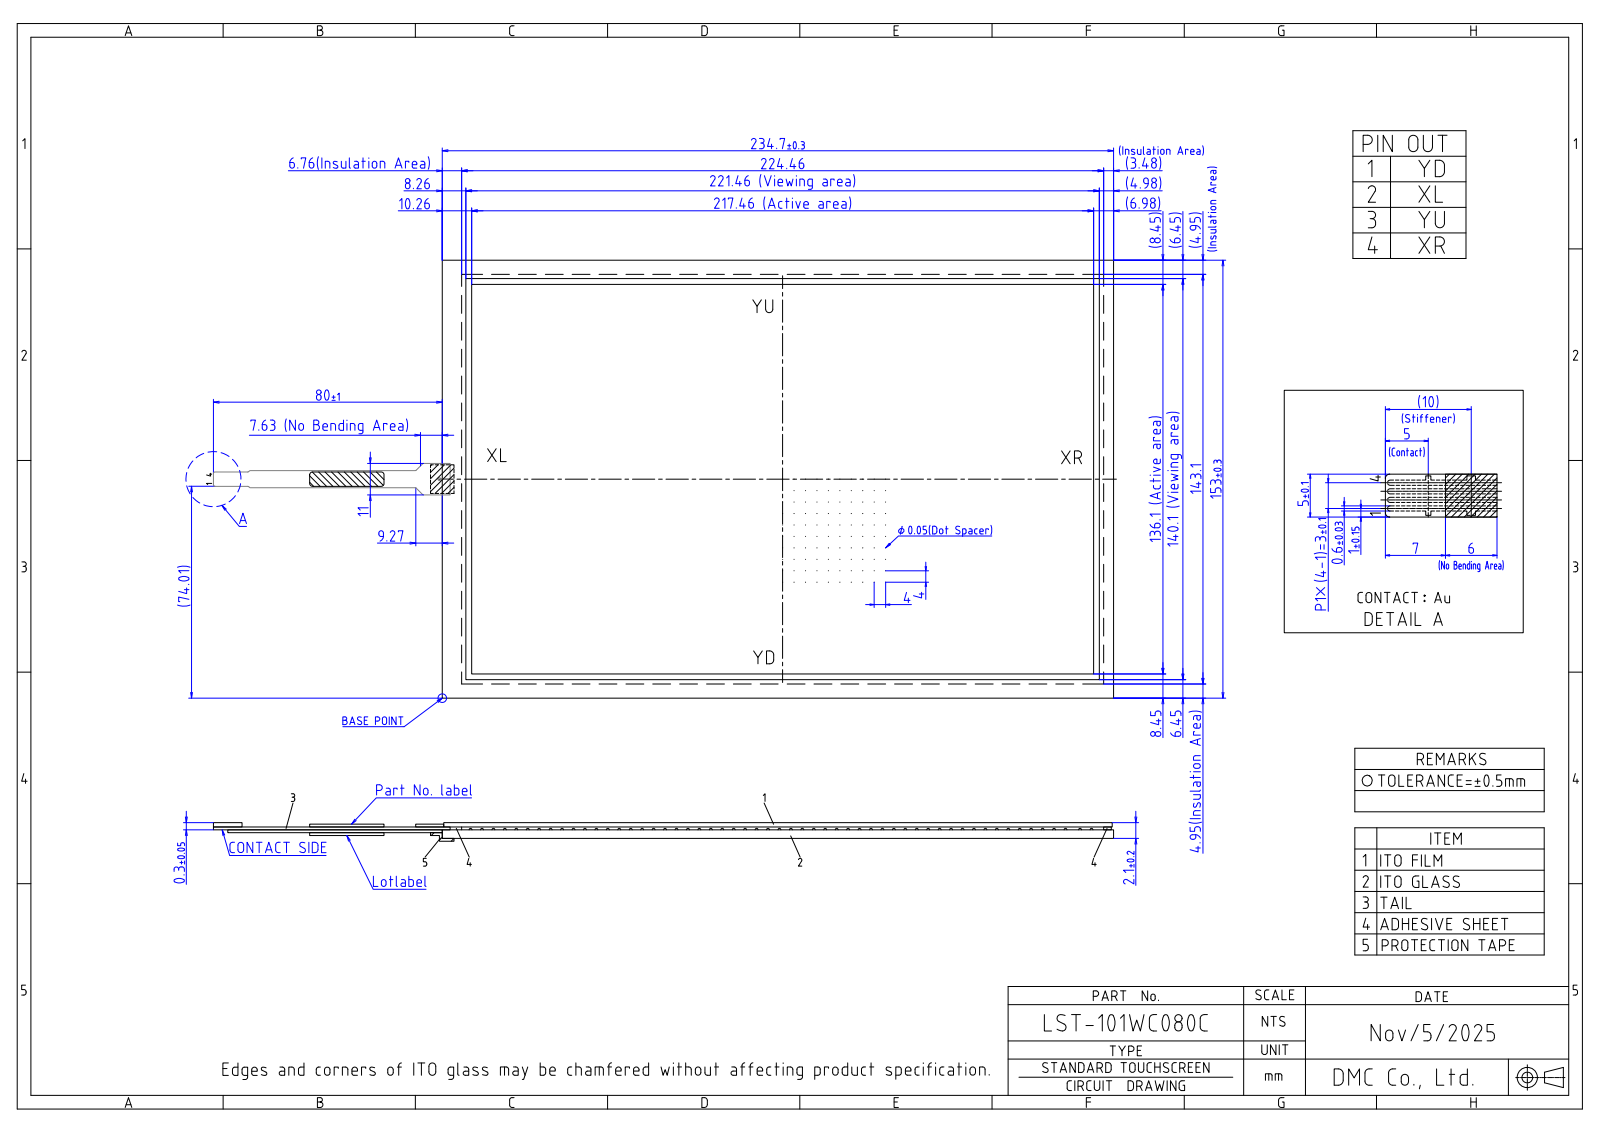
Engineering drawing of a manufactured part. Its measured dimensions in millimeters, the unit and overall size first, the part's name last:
Units: millimetres
Overall size (bounding box): 361.64 × 214.2 × 2.6
Partial cylindrical surfaces — rounded edges, fillets, slot ends (radius × count): R0.3 ×4, R0.5 ×2
Main face-to-face distances: 2.1, 2, 153, 2.2, 2.3, 234.7, 0.5, 0.6, 0.4, 2.6
Volume: 75 329 mm³ · Surface area: 74 623 mm²
Bodies: 2 solids, 52 faces (46 planar, 6 cylindrical, 0 other)
Part name (STEP PRODUCT): LST-101WC080C (3Dデータ)
STEP written by: Autodesk Inventor 2020 (CONFIG_CONTROL_DESIGN)
